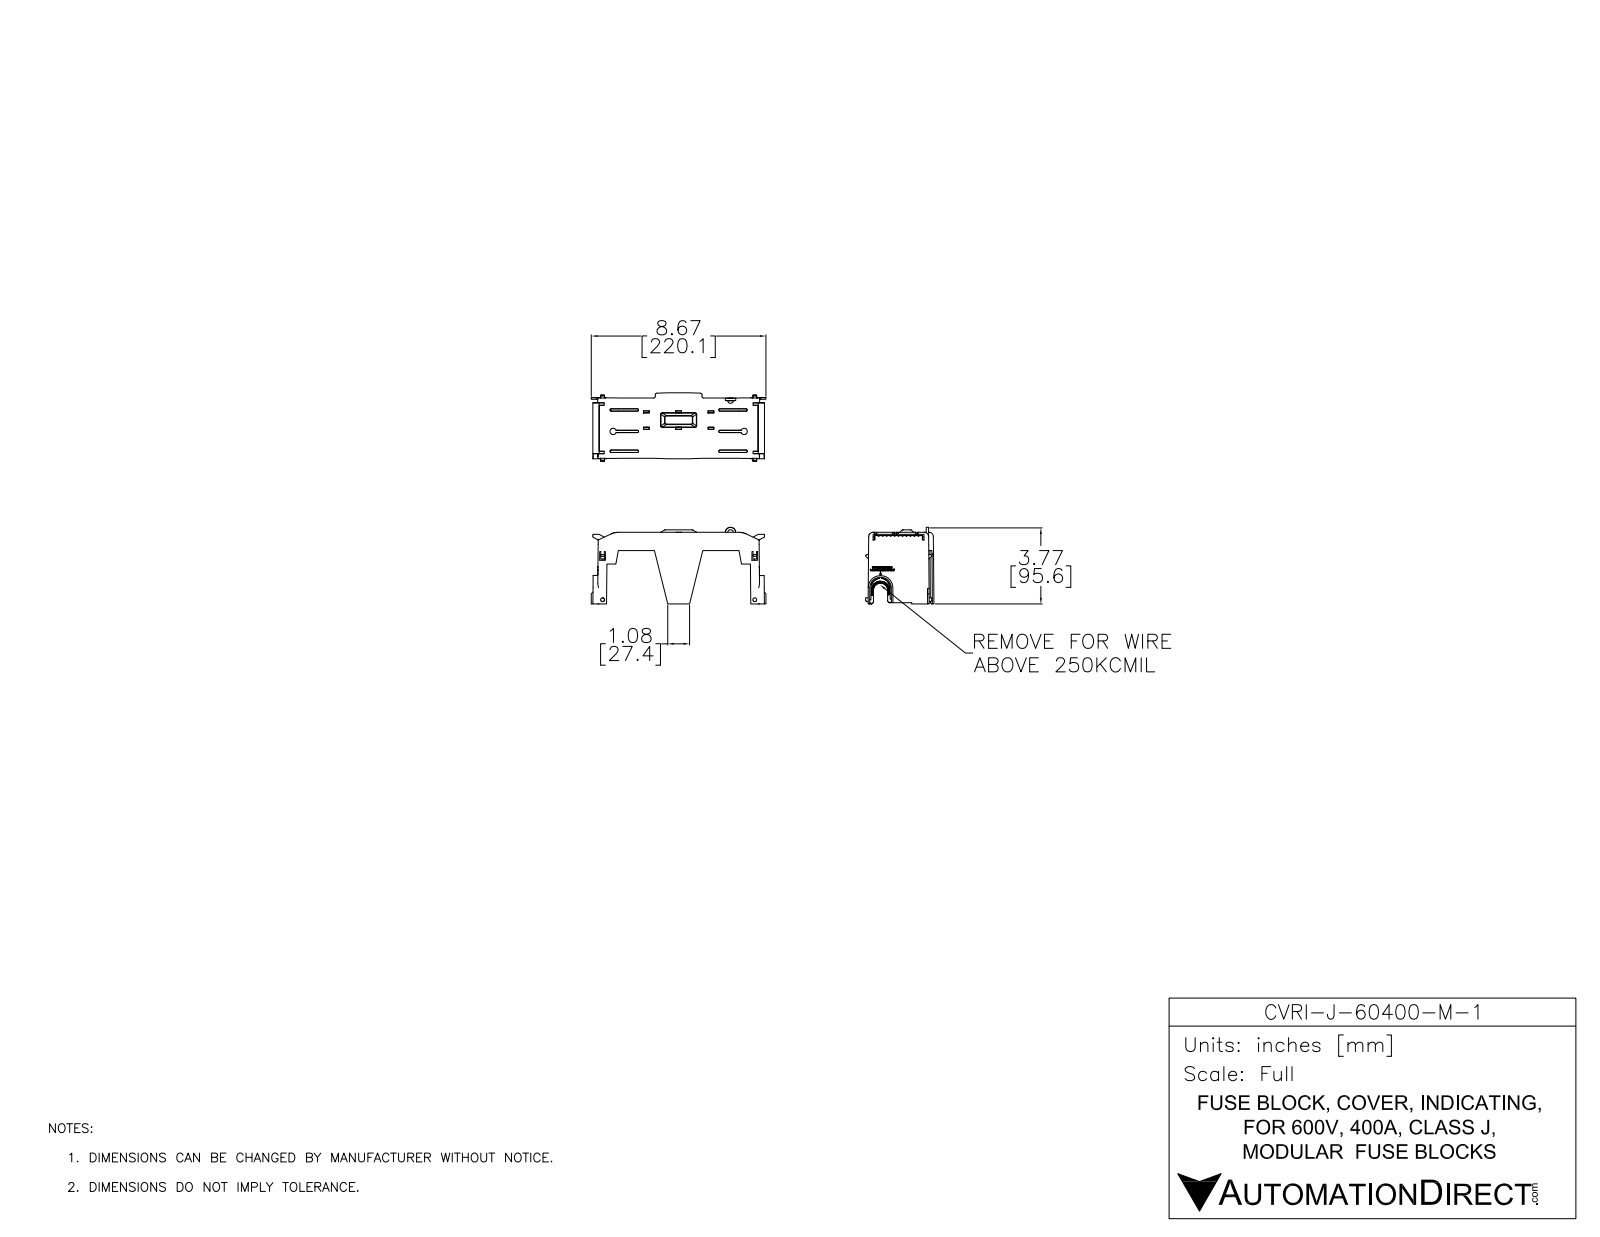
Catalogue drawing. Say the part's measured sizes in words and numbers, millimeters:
The part is named "CVRI-J-60400-M-1". Its 3-D file was written by "SolidWorks 2017 (AUTOMOTIVE_DESIGN)". It is 1 solid with 2395 faces: 1608 planar, 122 cylindrical and 665 other. Overall it measures 220.1 by 96.6 by 86.3 millimeters. Its volume is 104 800 cubic millimeters and its surface area 110 400 square millimeters. Round holes: 1 of diameter 7. Partial cylindrical surfaces (rounded edges, fillets, slot ends): 18 of radius 1, 11 of radius 3, 8 of radius 3.5, 7 of radius 5.5, 4 of radius 2, 2 of radius 0.3, 2 of radius 0.5, 2 of radius 1. The main face-to-face distances are 2, 6, 8, 4, 20.4, 3, 5, 17, 37.4, 88.3.
